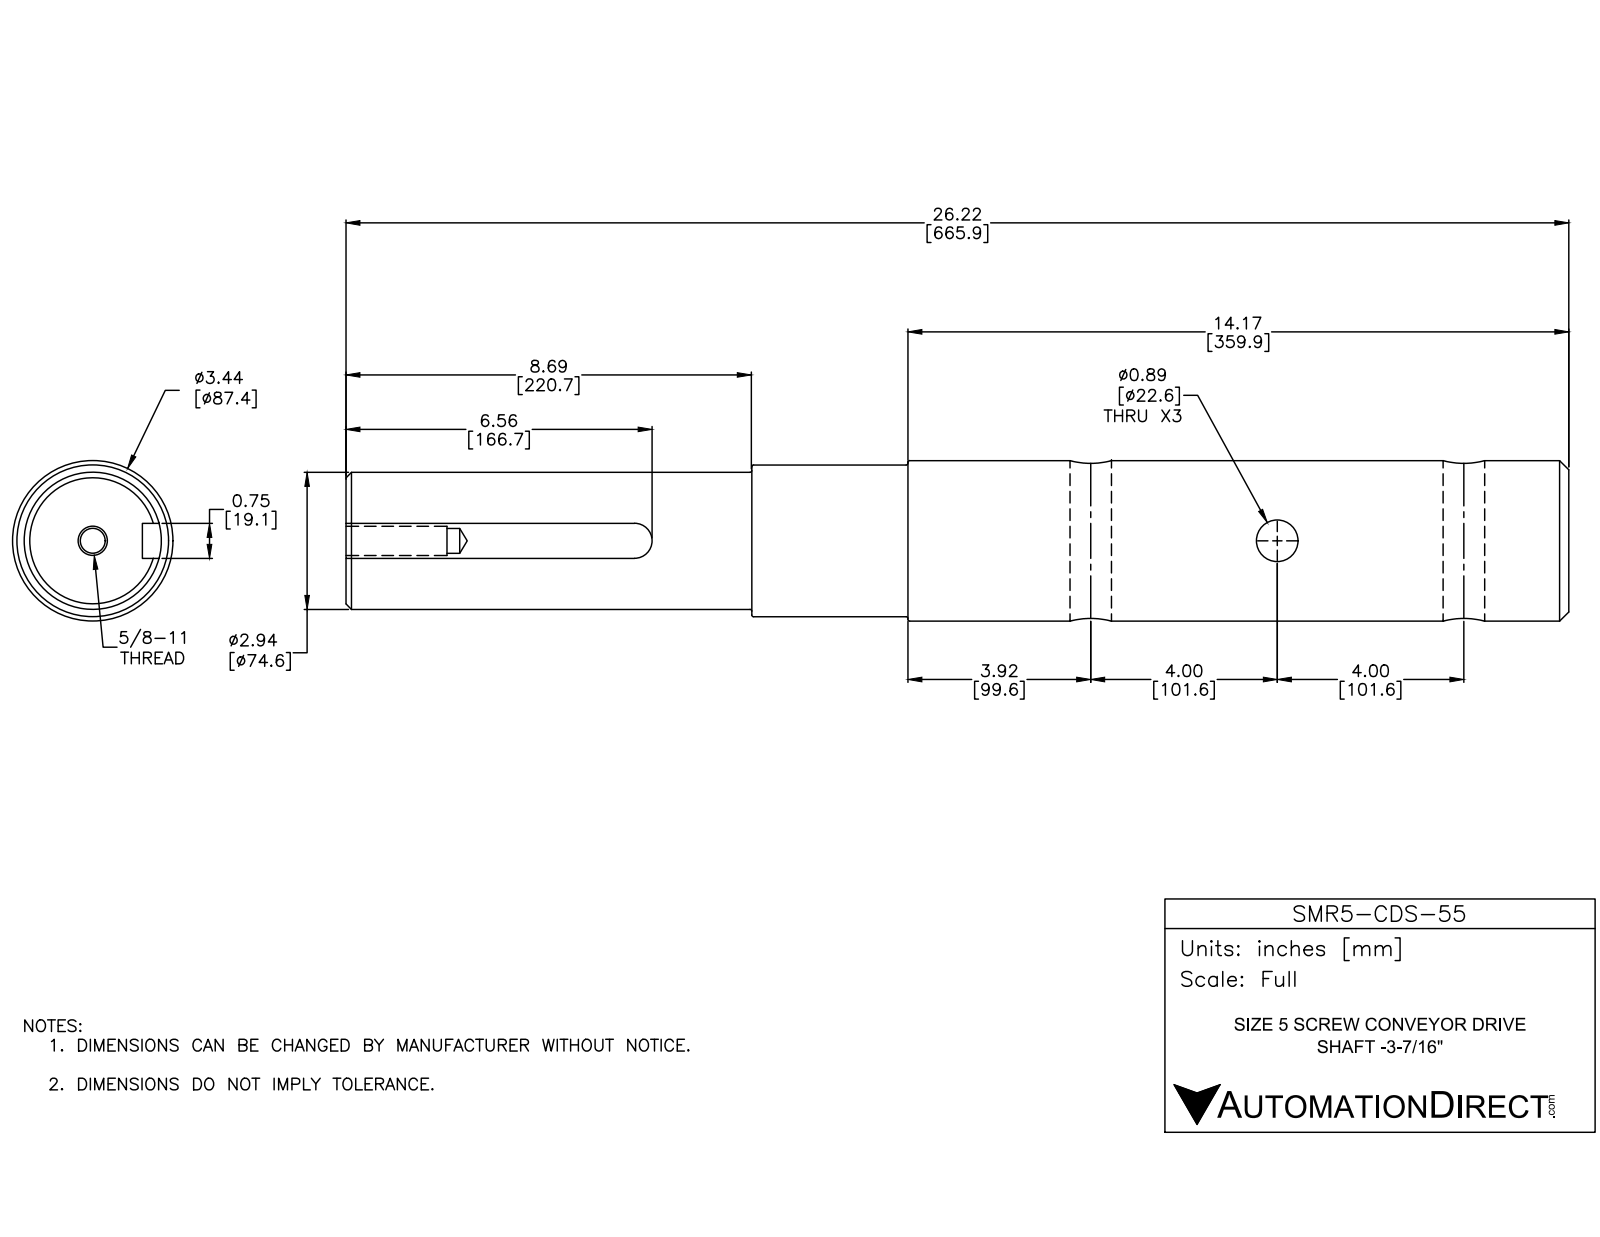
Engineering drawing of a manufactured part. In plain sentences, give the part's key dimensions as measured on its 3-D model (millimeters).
The part is named "SMR5-CDS-55". Its 3-D file was written by "SolidWorks 2016 (AUTOMOTIVE_DESIGN)". It is 1 solid with 40 faces: 8 planar, 18 cylindrical and 14 other. Overall it measures 665.9 by 87.4 by 87.4 millimeters. Its volume is 3 428 000 cubic millimeters and its surface area 204 800 square millimeters. Round holes: 3 of diameter 22.6, 1 of diameter 13.5, 1 of diameter 15.9. Round bosses or shafts: 1 of diameter 87.4, 1 of diameter 82.6, 1 of diameter 74.6. Partial cylindrical surfaces (rounded edges, fillets, slot ends): 1 of radius 9.5. The main face-to-face distances are 665.9, 19.1, 221, 444.9, 306, 85, 359.9, 55, 166, 251. The hole center spacings are 203.2.
